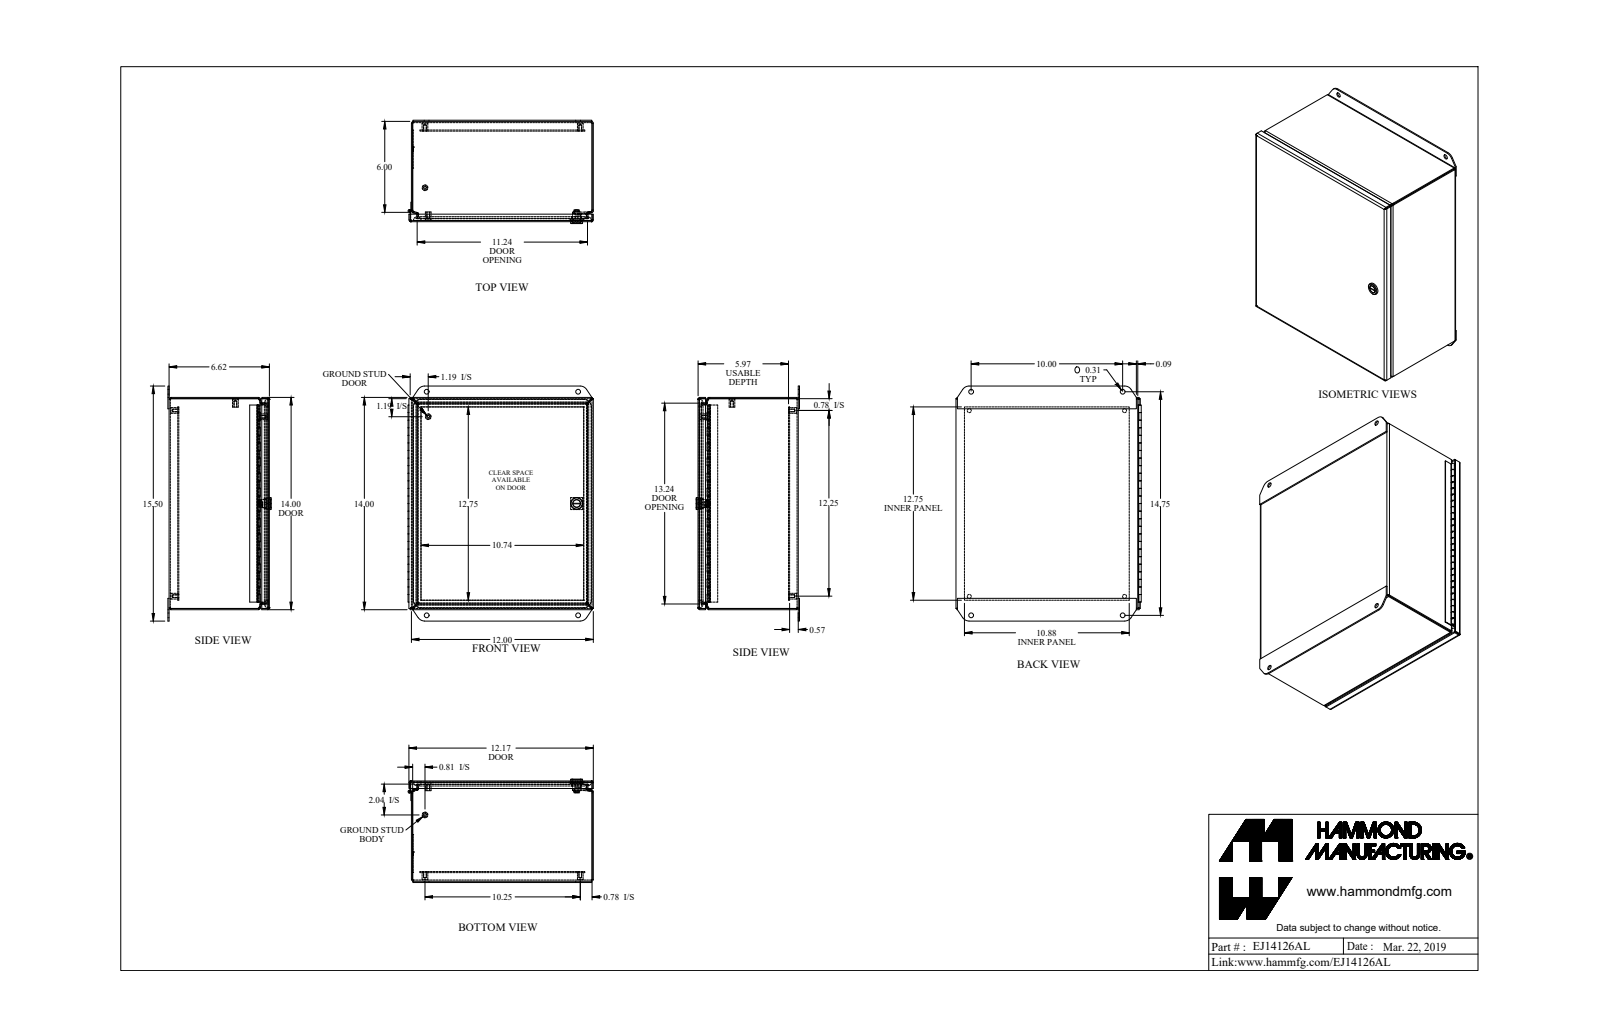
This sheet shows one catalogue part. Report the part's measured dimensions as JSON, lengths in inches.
{"part_name": "EJ14126AL_Default", "step_written_by": "SolidWorks 2019 (CONFIG_CONTROL_DESIGN)", "units": "inches", "bodies": {"solids": 14, "faces": 694, "planar": 466, "cylindrical": 160, "other": 68}, "overall_size": [15.5, 12.226, 6.82], "volume_in3": 75, "surface_area_in2": 1913, "round_holes": [[0.159, 6], [0.265, 4], [0.313, 4], [0.516, 1]], "round_bosses_or_shafts": [[0.375, 6], [0.33, 6], [0.788, 1], [0.535, 1], [0.496, 1], [0.435, 1], [0.18, 1], [0.1, 1]], "partial_cylinders_radius": [[0.041, 16], [0.121, 16], [0.281, 12], [0.25, 4], [0.499, 4], [0.5, 4], [0.06, 2], [0.03, 1]], "face_to_face_distances": [0.081, 6.536, 6.617, 11.919, 6.455, 13.919, 0.643, 0.562, 5.974, 5.893], "hole_center_spacings": [1.257, 10.202, 13.5, 15.972, 16.875, 0.024, 6.129, 7.376]}
